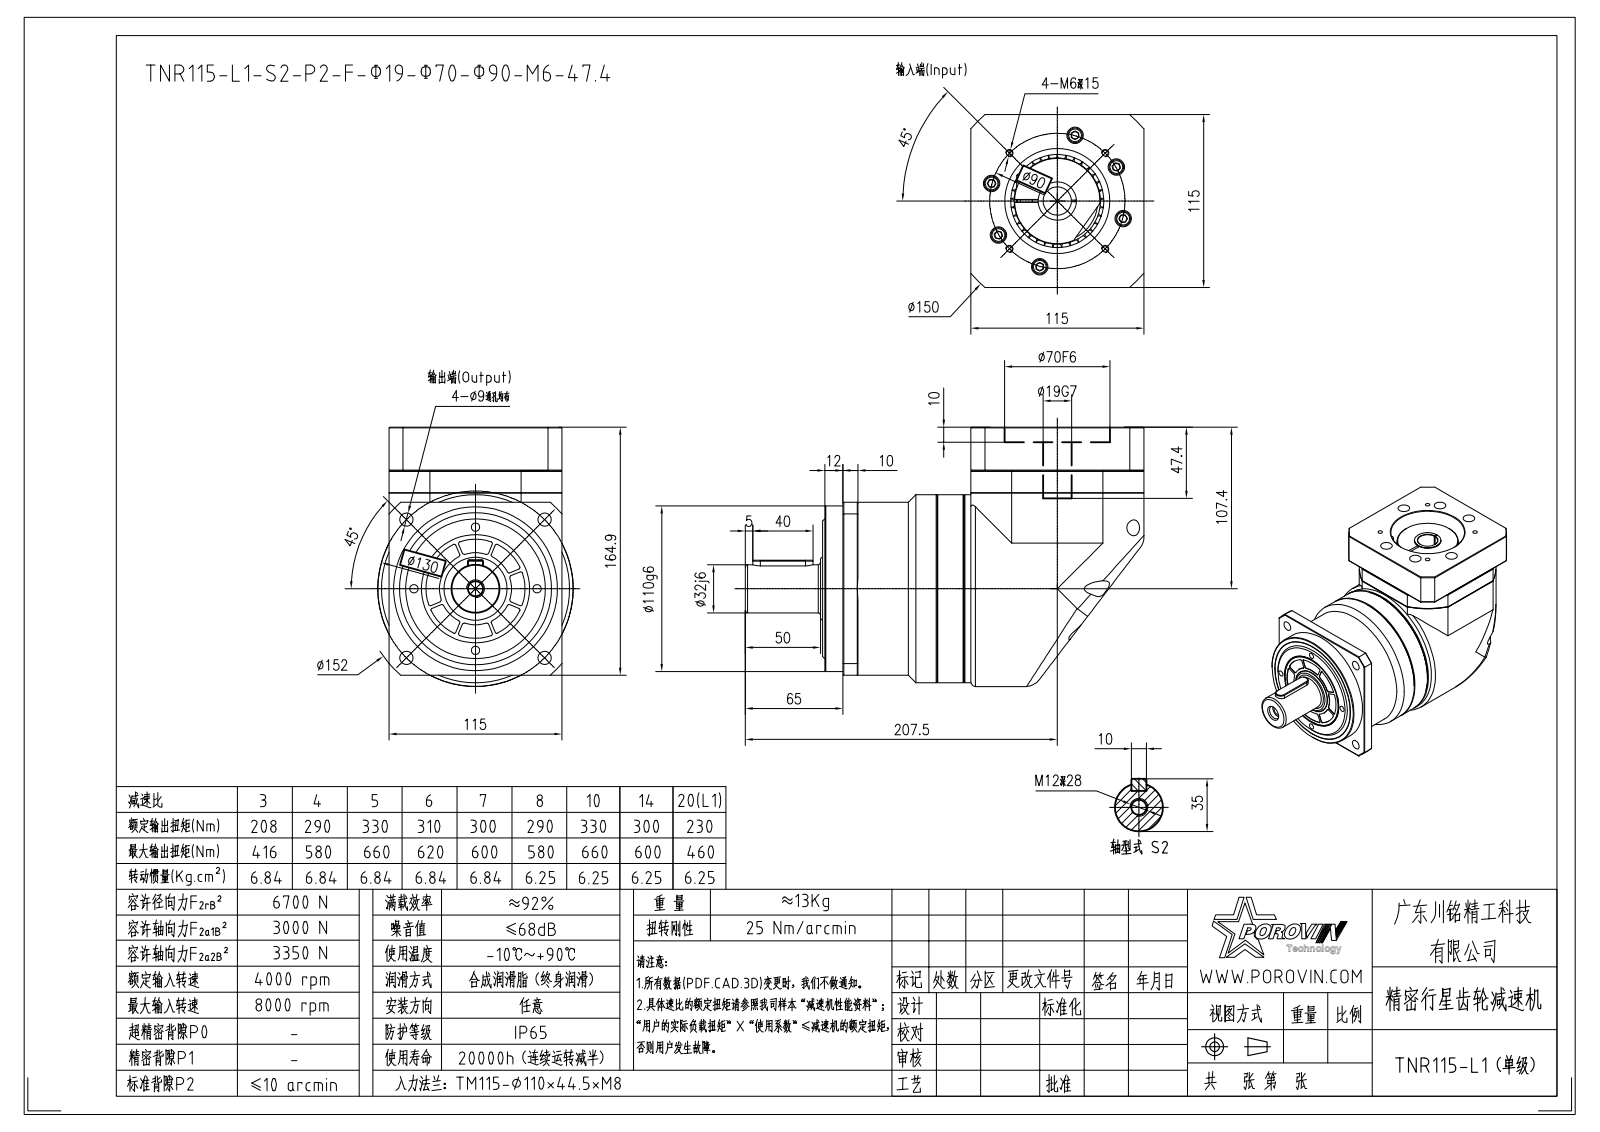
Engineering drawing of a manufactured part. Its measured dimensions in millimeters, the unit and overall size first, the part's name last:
Units: millimetres
Overall size (bounding box): 265 × 172.4 × 130
Round holes (diameter × count): ⌀6.68 ×19, ⌀6.5 ×13, ⌀5 ×12, ⌀11 ×12, ⌀10.5 ×7, ⌀6.6 ×6, ⌀5.5 ×4, ⌀6 ×4, ⌀9 ×4, ⌀72 ×2, ⌀6.8 ×1, ⌀8.5 ×1
Round bosses / shafts (diameter × count): ⌀10 ×19, ⌀9.88 ×19, ⌀6 ×19, ⌀130 ×1, ⌀125 ×1, ⌀124 ×1, ⌀115 ×1, ⌀110 ×1
Partial cylindrical surfaces — rounded edges, fillets, slot ends (radius × count): R1 ×64, R5 ×3, R6.75 ×1, R10 ×1, R65 ×1, R75 ×1, R76 ×1
Main face-to-face distances: 18, 17.8, 14.9, 43.9, 29, 115, 3, 5, 71, 88.8
Hole centre spacings: 45.25, 57.25, 35.47, 46.18, 83.61, 85.46, 98.8, 46.42
Volume: 2 778 000 mm³ · Surface area: 335 307 mm²
Bodies: 50 solids, 1418 faces (582 planar, 570 cylindrical, 266 other)
Part name (STEP PRODUCT): SPRING_LOCK_WASHERS--NORMAL_TYP; TNR115190001_1; HEXAGON_SOCKET_HEAD_CAP_S-22522; 65X55X700_1 (+8 more)
STEP written by: CREO PARAMETRIC BY PTC INC, 2020053 (CONFIG_CONTROL_DESIGN)
